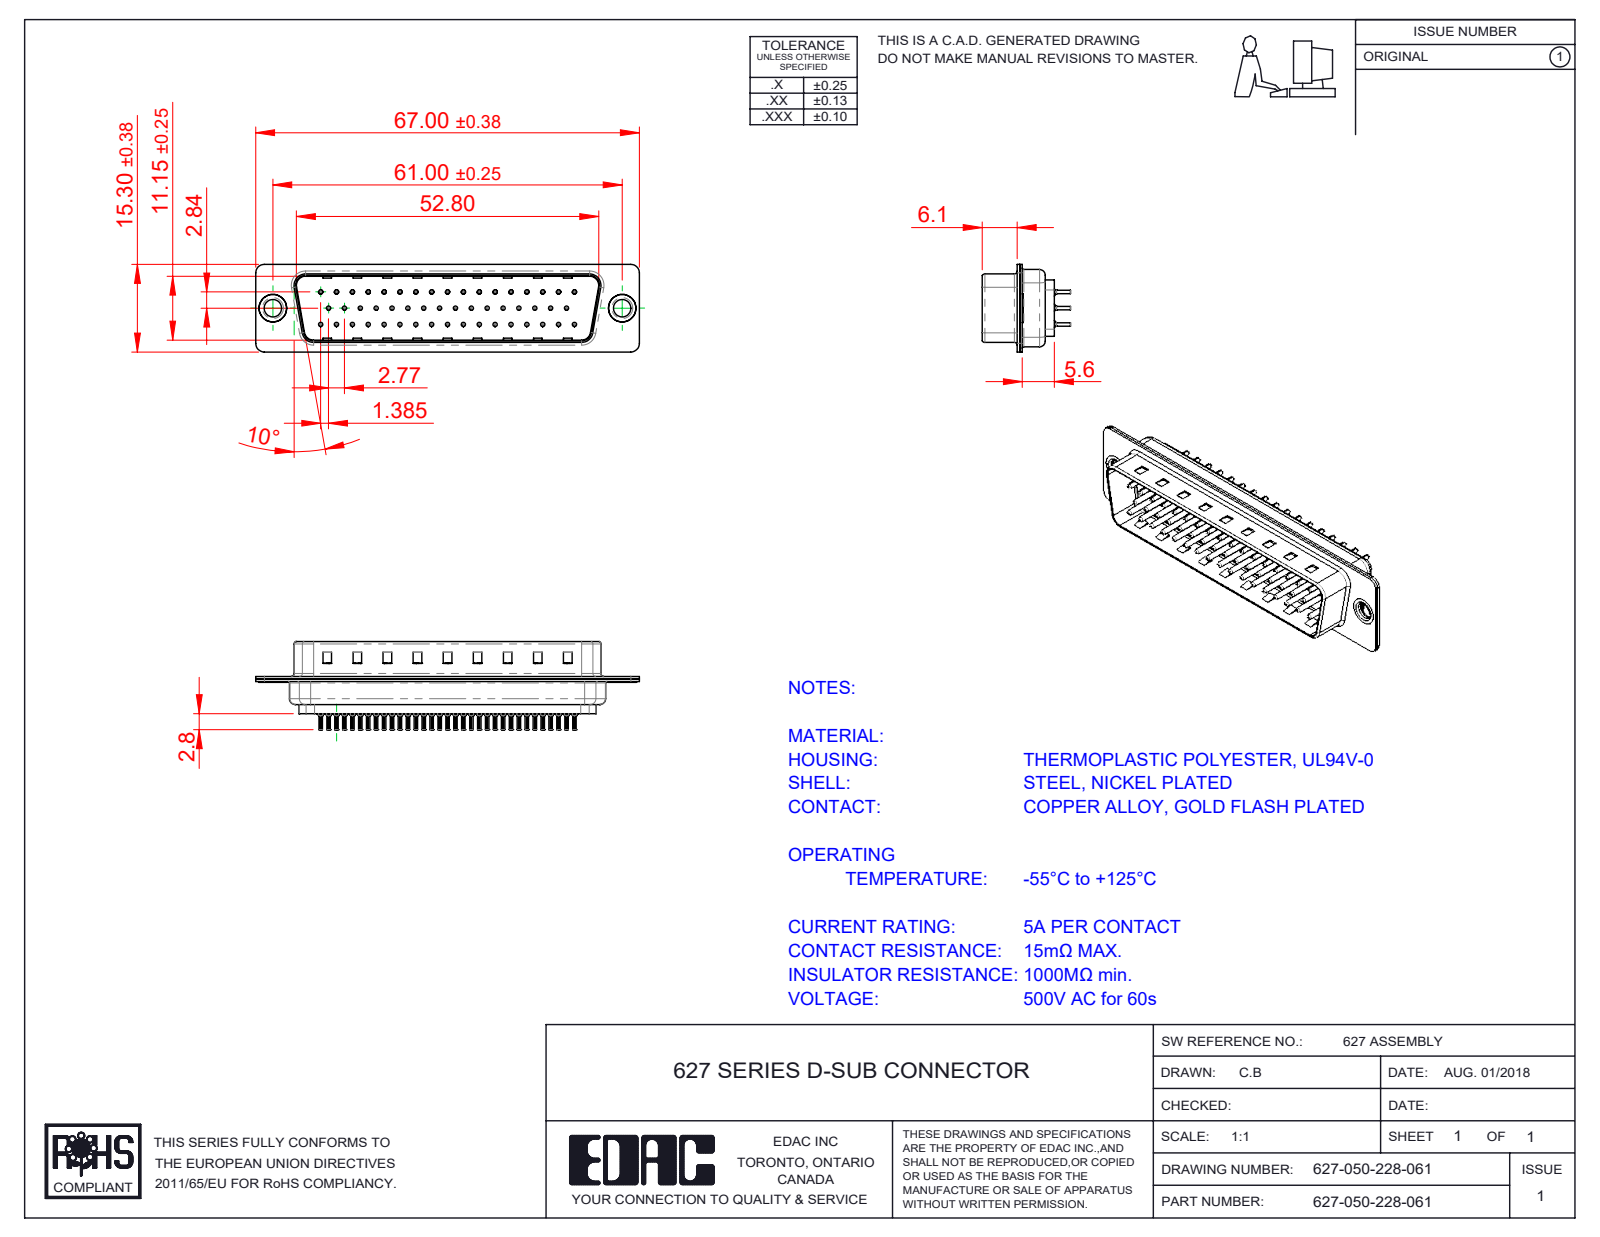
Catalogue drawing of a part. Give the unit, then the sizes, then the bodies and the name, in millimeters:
Units: millimetres
Overall size (bounding box): 67 × 18.8 × 15.3
Round holes (diameter × count): ⌀0.2 ×50, ⌀0.35 ×50, ⌀1.1 ×50, ⌀1.6 ×50, ⌀3.05 ×2, ⌀4 ×2, ⌀4.8 ×2
Round bosses / shafts (diameter × count): ⌀2 ×50, ⌀1.5 ×50, ⌀0.75 ×50, ⌀0.6 ×50, ⌀5 ×2, ⌀4.9 ×2, ⌀3.55 ×2
Partial cylindrical surfaces — rounded edges, fillets, slot ends (radius × count): R0.1 ×100, R1.5 ×16, R2 ×12, R0.5 ×8, R1.6 ×8, R0.25 ×4, R0.6 ×4, R0.65 ×4
Main face-to-face distances: 0.4, 6.05, 0.45, 11.55, 0.9, 2.8, 8.85, 9.3, 6.5, 0.78
Hole centre spacings: 2.77, 3.16, 5.54, 8.31, 11.08, 13.85, 16.62, 19.39
Volume: 5 477 mm³ · Surface area: 14 486 mm²
Bodies: 56 solids, 5397 faces (1409 planar, 2080 cylindrical, 1908 other)
Part name (STEP PRODUCT): 627 Contact Row 3_28L; 627 Housing_50 FF; 627-050-228-061; 627 Shell Front_50 Contacts (+4 more)
STEP written by: SolidWorks 2020 (CONFIG_CONTROL_DESIGN)
